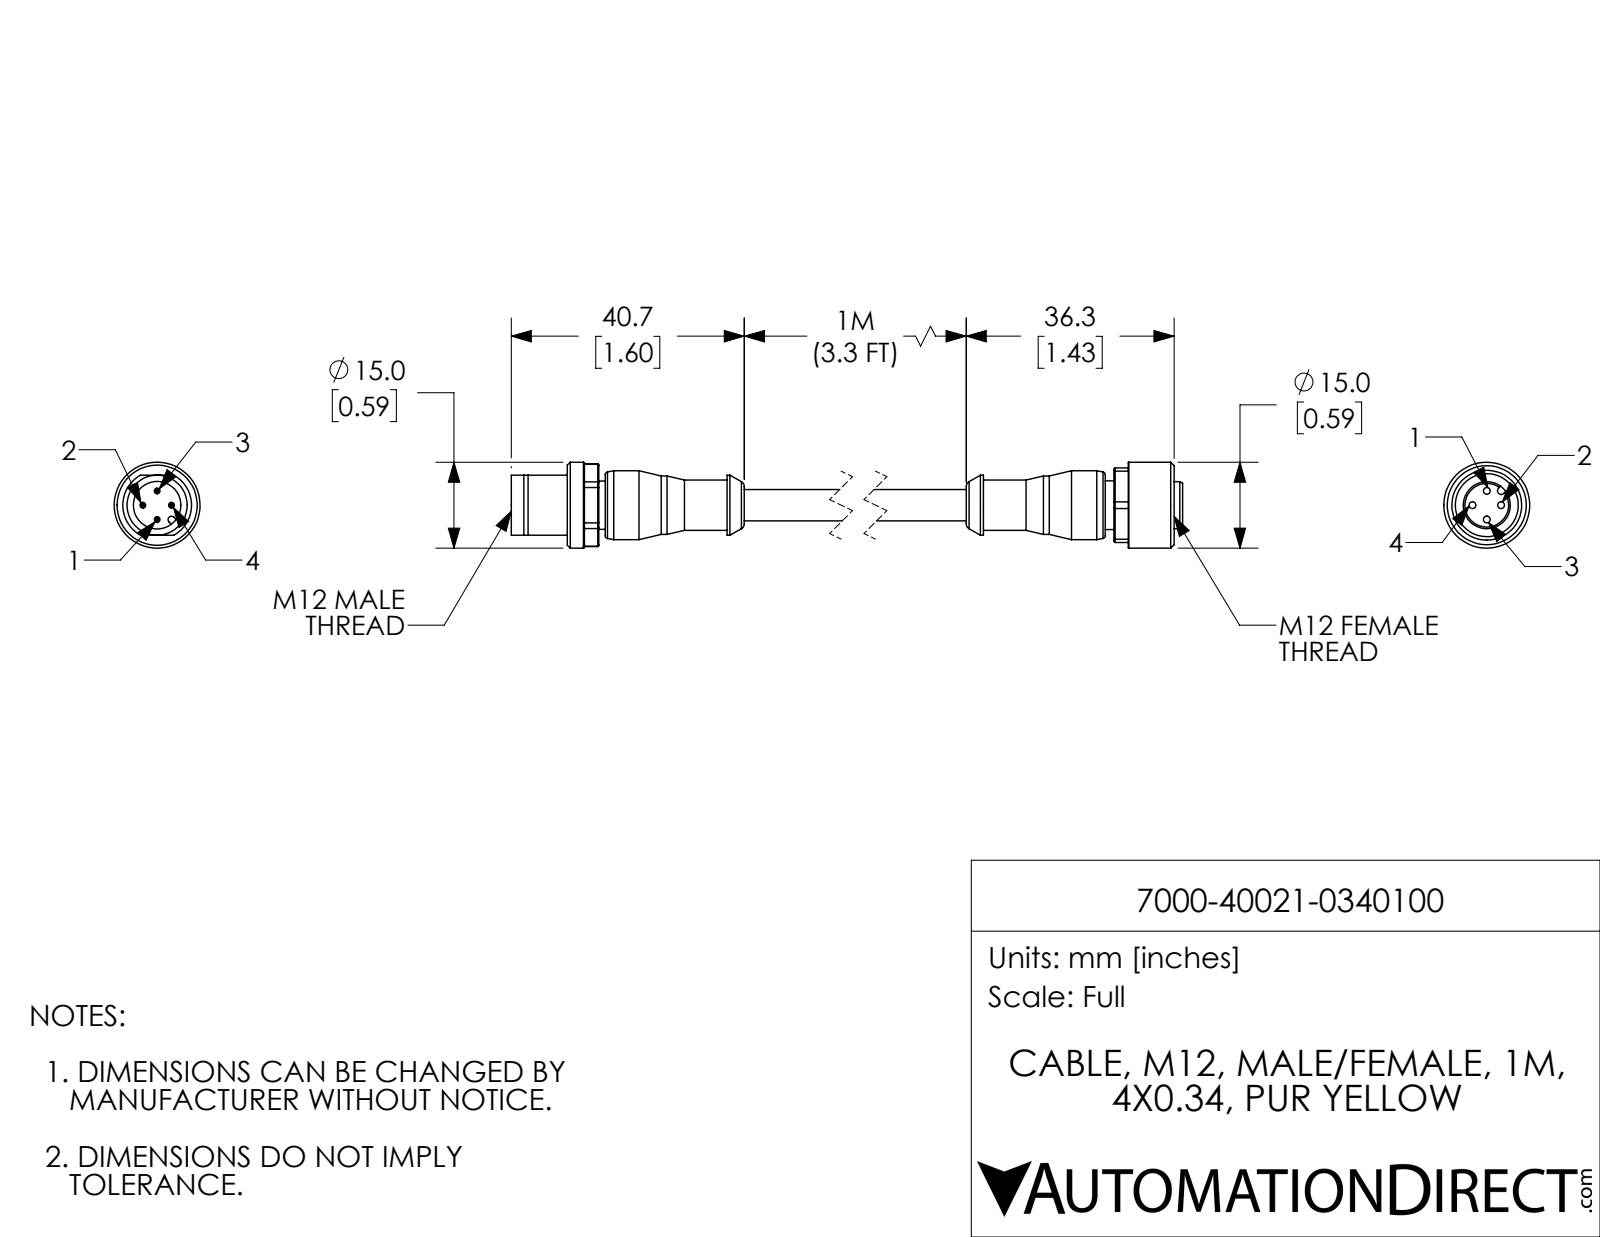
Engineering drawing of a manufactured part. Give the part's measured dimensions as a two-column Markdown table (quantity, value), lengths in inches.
| quantity | value |
| --- | --- |
| part name | 7000-40021-0340100; 7000-40021-0340100_MALE; 7000-40021-0340100_FEMALE |
| STEP written by | SolidWorks 2021 (CONFIG_CONTROL_DESIGN) |
| units | inches |
| bodies | 2 solids, 188 faces (58 planar, 69 cylindrical, 61 other) |
| overall size | 5.138 × 0.591 × 0.591 |
| volume | 0.488 in³ |
| surface area | 7.93 in² |
| round holes (diameter × count) | 0.047 × 4, 0.327 × 1, 0.433 × 1 |
| round bosses / shafts (diameter × count) | 0.039 × 4, 0.591 × 1, 0.472 × 1, 0.413 × 1, 0.402 × 1, 0.346 × 1, 0.335 × 1, 0.331 × 1 |
| partial cylindrical surfaces (radius × count) | 0.024 × 1, 0.026 × 1, 0.283 × 1 |
| main face-to-face distances | 0.472, 0.512, 0.118, 4.063, 0.413, 4.433, 2.217, 4.28, 0.295, 0.059 |
| hole center spacings | 0.098, 0.139, 0.197 |
